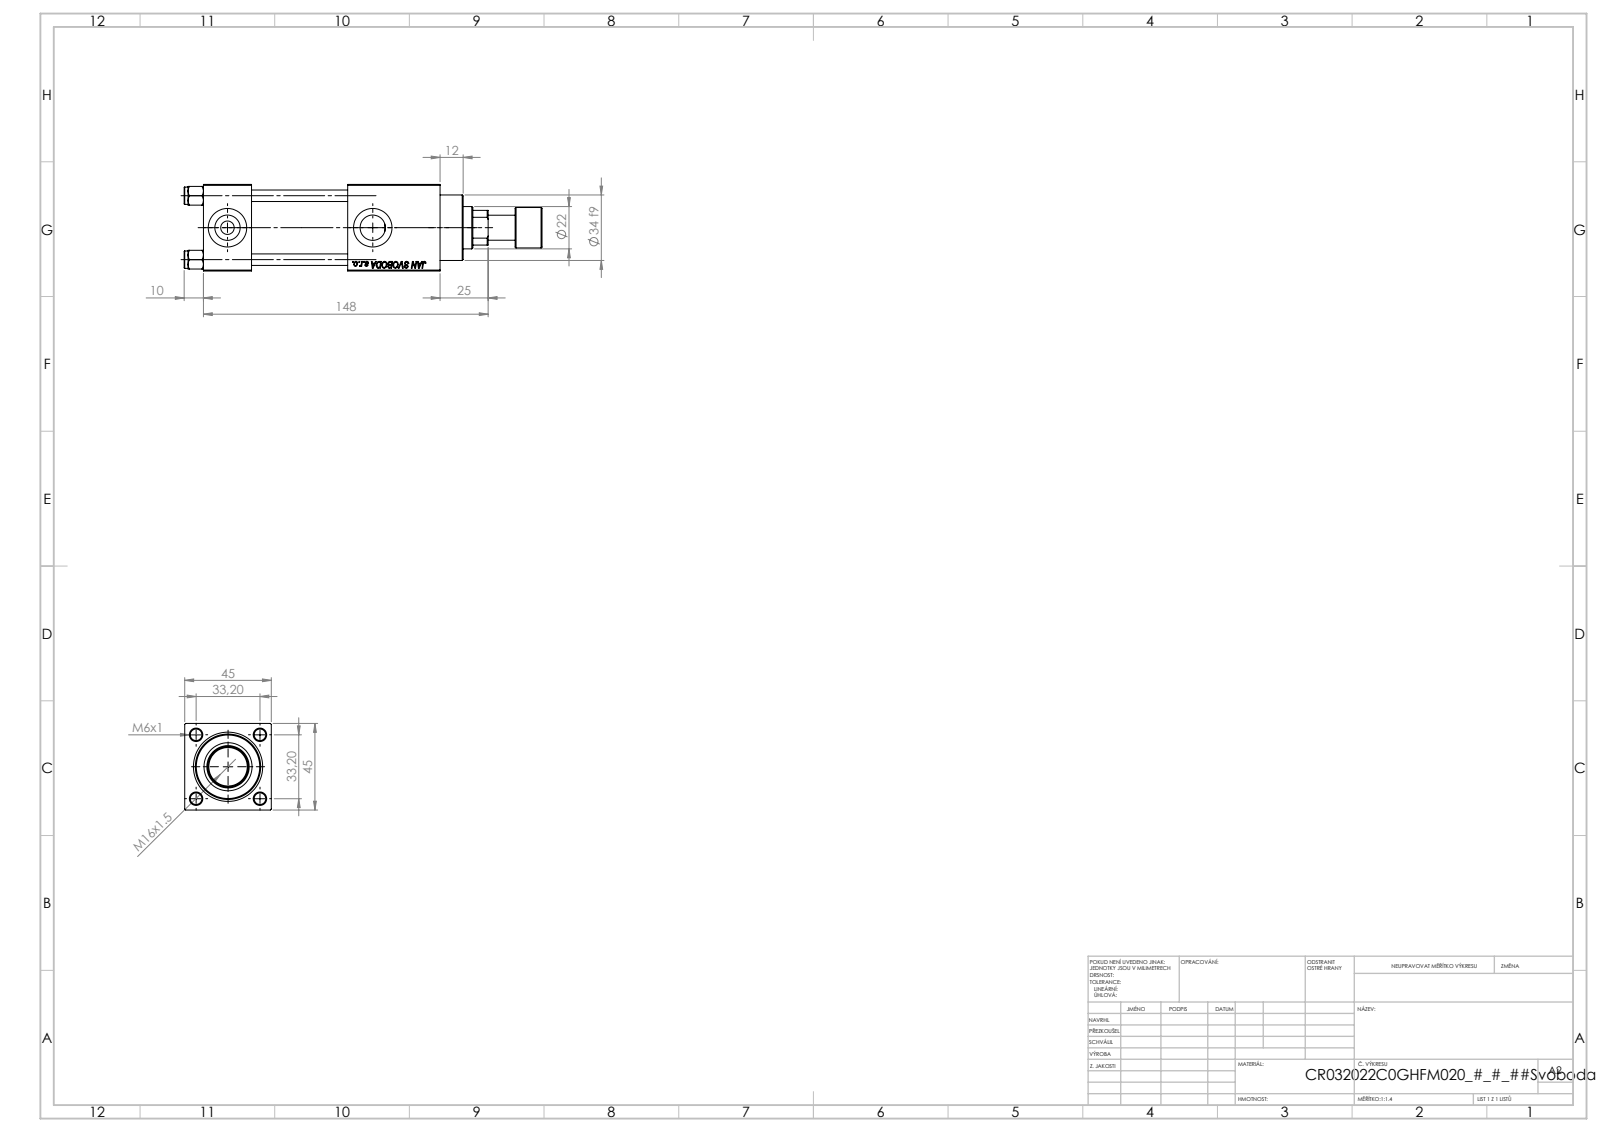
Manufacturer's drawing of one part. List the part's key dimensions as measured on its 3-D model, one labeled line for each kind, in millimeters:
Part name (STEP PRODUCT): V215CR_C_Body; V215CR_C_TYCINKA; V215_VC_A; NUT_M5_C (+2 more)
STEP written by: SolidWorks 2019 (CONFIG_CONTROL_DESIGN)
Units: millimetres
Bodies: 12 solids, 1158 faces (528 planar, 90 cylindrical, 540 other)
Overall size (bounding box): 186 × 45 × 45
Volume: 216 560 mm³ · Surface area: 73 462 mm²
Round holes (diameter × count): ⌀6 ×4, ⌀7 ×2, ⌀13.16 ×2, ⌀20 ×2, ⌀10.5 ×1, ⌀22 ×1, ⌀24 ×1, ⌀25 ×1, ⌀32 ×1, ⌀33 ×1
Round bosses / shafts (diameter × count): ⌀9 ×4, ⌀38 ×1, ⌀34 ×1, ⌀21 ×1, ⌀13 ×1
Main face-to-face distances: 45, 25, 123, 50, 75, 98, 48, 94.3, 69.3, 19.3
Hole centre spacings: 23.48, 33.2, 46.95, 75.5
